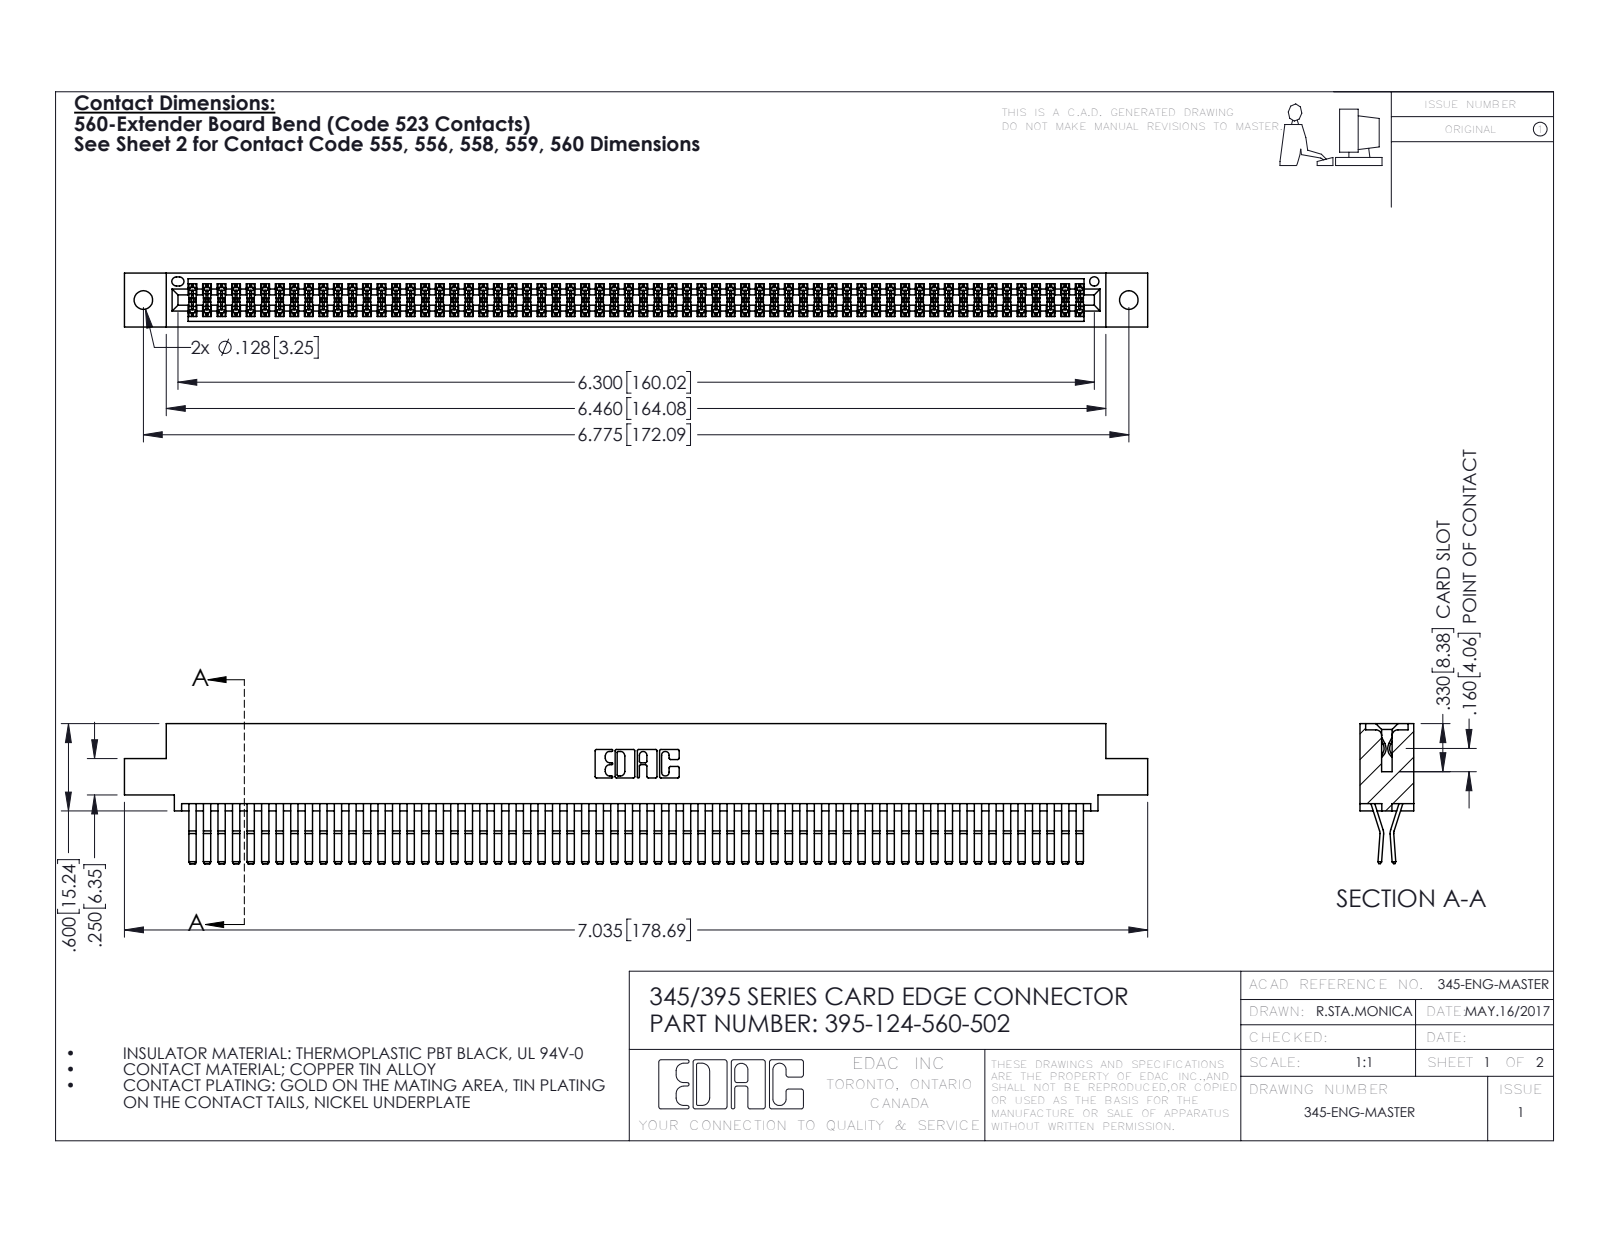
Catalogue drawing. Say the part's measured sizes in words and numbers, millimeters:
The part is named "395-124-560-502; 345-292-001_560 Tail; 345 Part_0.110 Offset - 0.128 Dia". Its 3-D file was written by "SolidWorks 2016 (CONFIG_CONTROL_DESIGN)". It is 125 solids with 6578 faces: 4176 planar, 2402 cylindrical and 0 other. Overall it measures 178.7 by 24.4 by 9.4 millimeters. Its volume is 18 240 cubic millimeters and its surface area 29 270 square millimeters. Round holes: 2 of diameter 3.3, 1 of diameter 1.6. Partial cylindrical surfaces (rounded edges, fillets, slot ends): 187 of radius 0.2, 22 of radius 0.3, 6 of radius 0.2, 6 of radius 0.8, 3 of radius 0.7, 2 of radius 0.3, 2 of radius 0.4, 2 of radius 0.5. The main face-to-face distances are 0.6, 7.6, 1.8, 9.4, 5.1, 2.5, 6.9, 5.7, 4.4, 3.8. The hole center spacings are 6.9, 166.1, 172.1.
